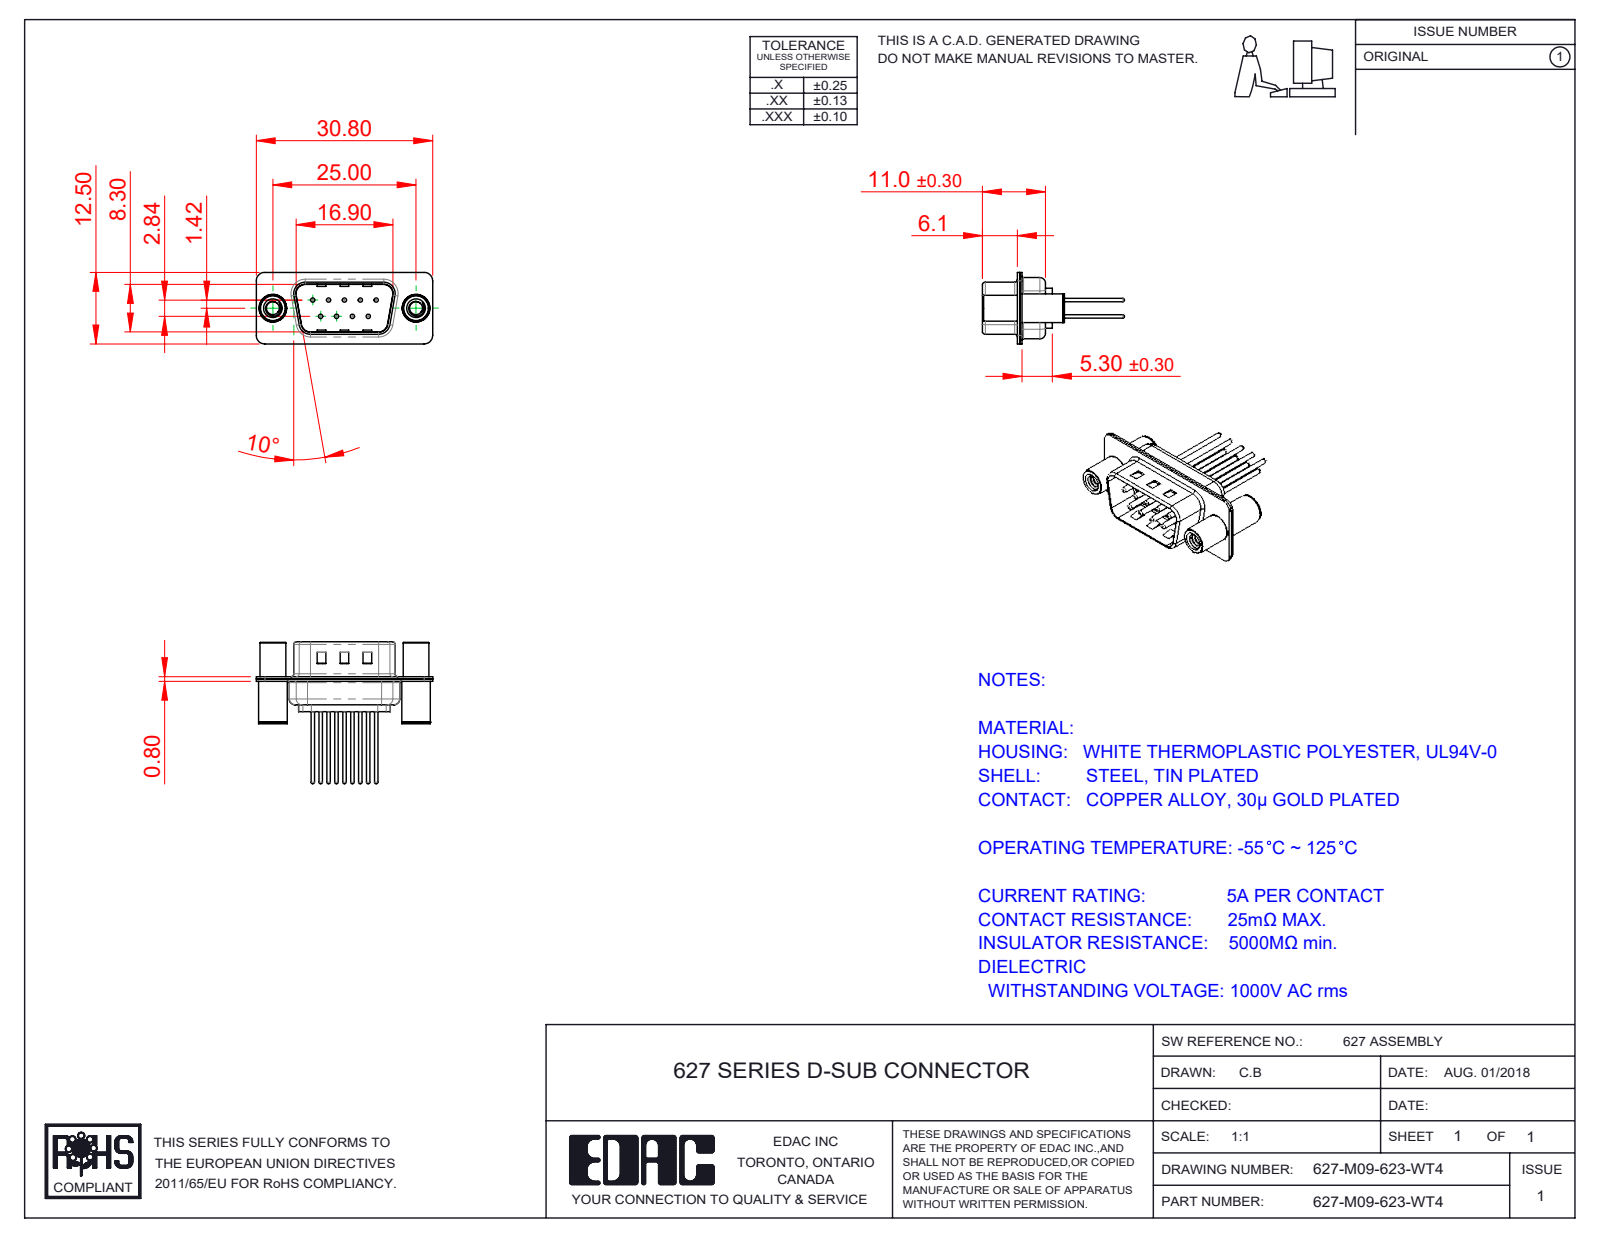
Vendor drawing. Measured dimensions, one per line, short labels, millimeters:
name: 627M Housing_09 Contacts; 627-M09-623-WT4; 627M Shell Front_09 Contacts; 627M Contact Row 1_23 (+3 more)
written by: SolidWorks 2020 (CONFIG_CONTROL_DESIGN)
unit: mm
bodies: 14 solids, 723 faces (176 planar, 307 cylindrical, 240 other)
size: 30.8 × 24.77 × 12.5
volume: 1 615 mm³; area: 4 220 mm²
holes: 9× ⌀0.75, 9× ⌀1.6, 9× ⌀2, 2× ⌀2.26, 2× ⌀3.26, 2× ⌀4, 2× ⌀4.8
bosses: 9× ⌀1.5, 9× ⌀0.6, 2× ⌀5, 2× ⌀4.9, 2× ⌀4.5
rounds: 16× R1.5, 12× R2, 8× R0.5, 8× R1.6, 4× R0.25, 4× R0.6, 4× R0.65, 4× R0.9
face distances: 0.4, 0.8, 9.5, 9.1, 8.7, 0.65, 9.9, 1.2, 5.3, 6.1
hole spacings: 3.16, 2.77, 5.54, 5.03, 5.04, 8.31, 7.1, 7.48
